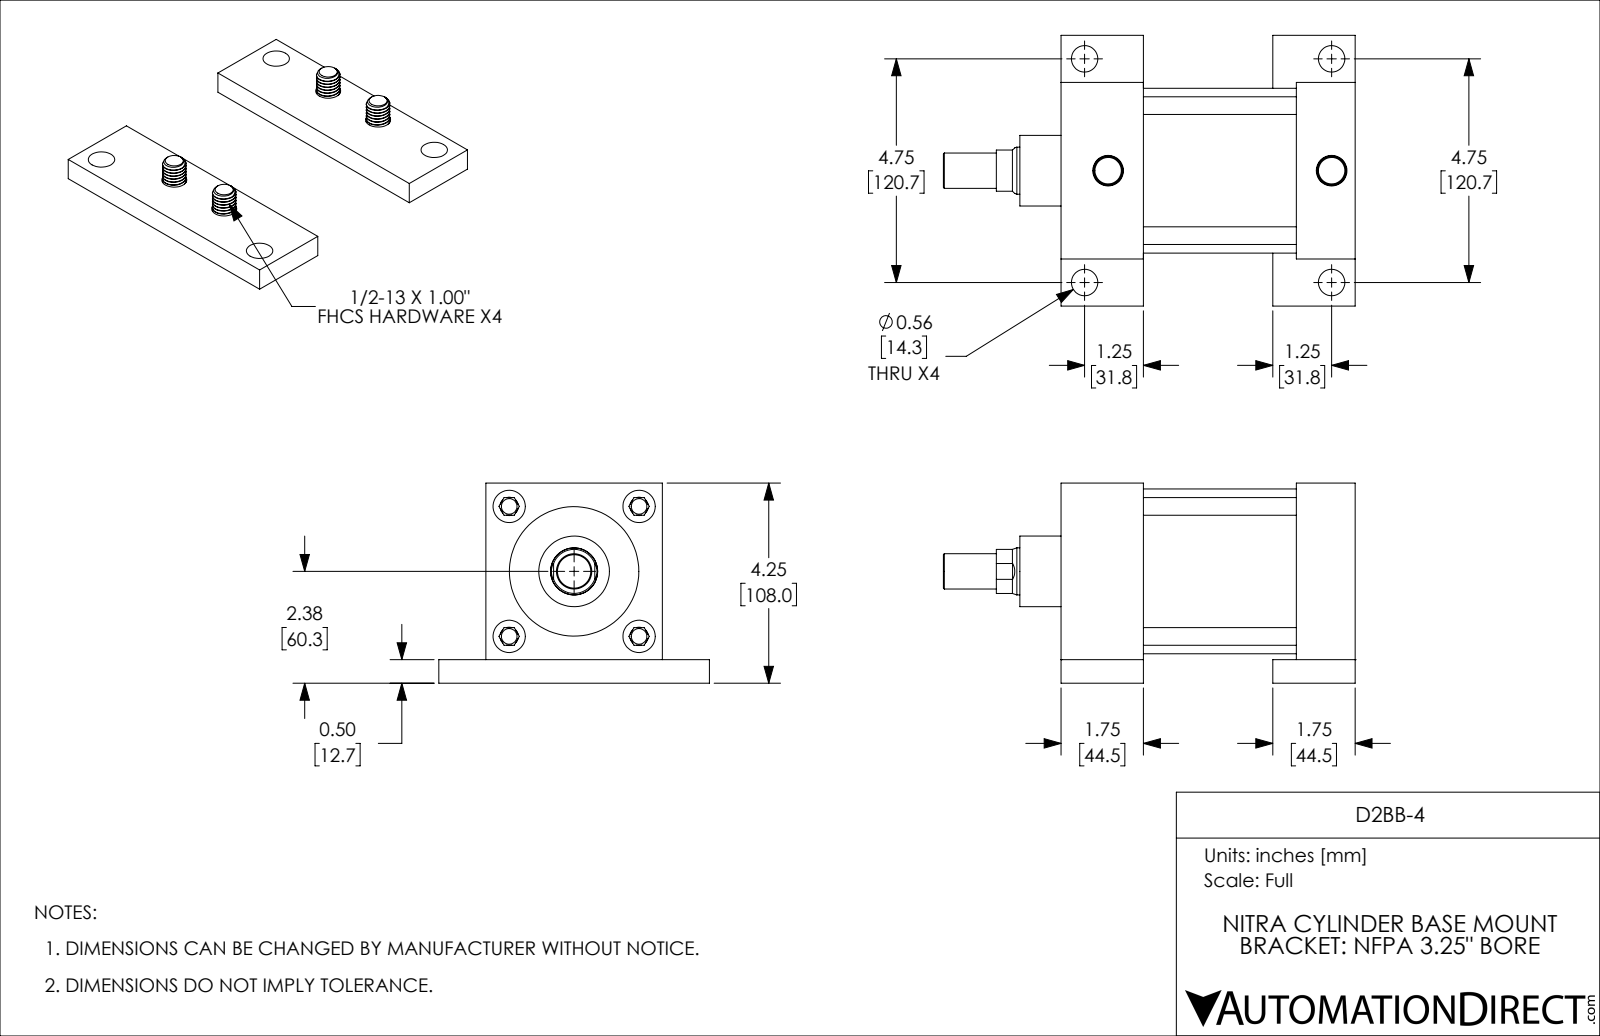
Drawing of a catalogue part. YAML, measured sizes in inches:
part_name: "D2BB-4; D2BB-4_2; D2BB-4_1"
step_written_by: "SolidWorks 2019 (CONFIG_CONTROL_DESIGN)"
units: inches
bodies: {solids: 6, faces: 304, planar: 48, cylindrical: 172, other: 84}
overall_size: [6.249, 5.75, 1]
volume: 9.793
surface_area: 72.01
round_holes:
  - {diameter: 0.531, count: 4}
  - {diameter: 0.562, count: 4}
round_bosses_or_shafts:
  - {diameter: 0.938, count: 4}
  - {diameter: 0.5, count: 4}
  - {diameter: 0.4, count: 4}
face_to_face_distances: [0.5, 1.75, 4.499, 6.249, 2.749, 5.75, 1, 0.313, 0.176, 0.324]
hole_center_spacings: [1.5, 1.626, 3.126, 4.625, 4.862, 4.961, 5.249, 5.633]
